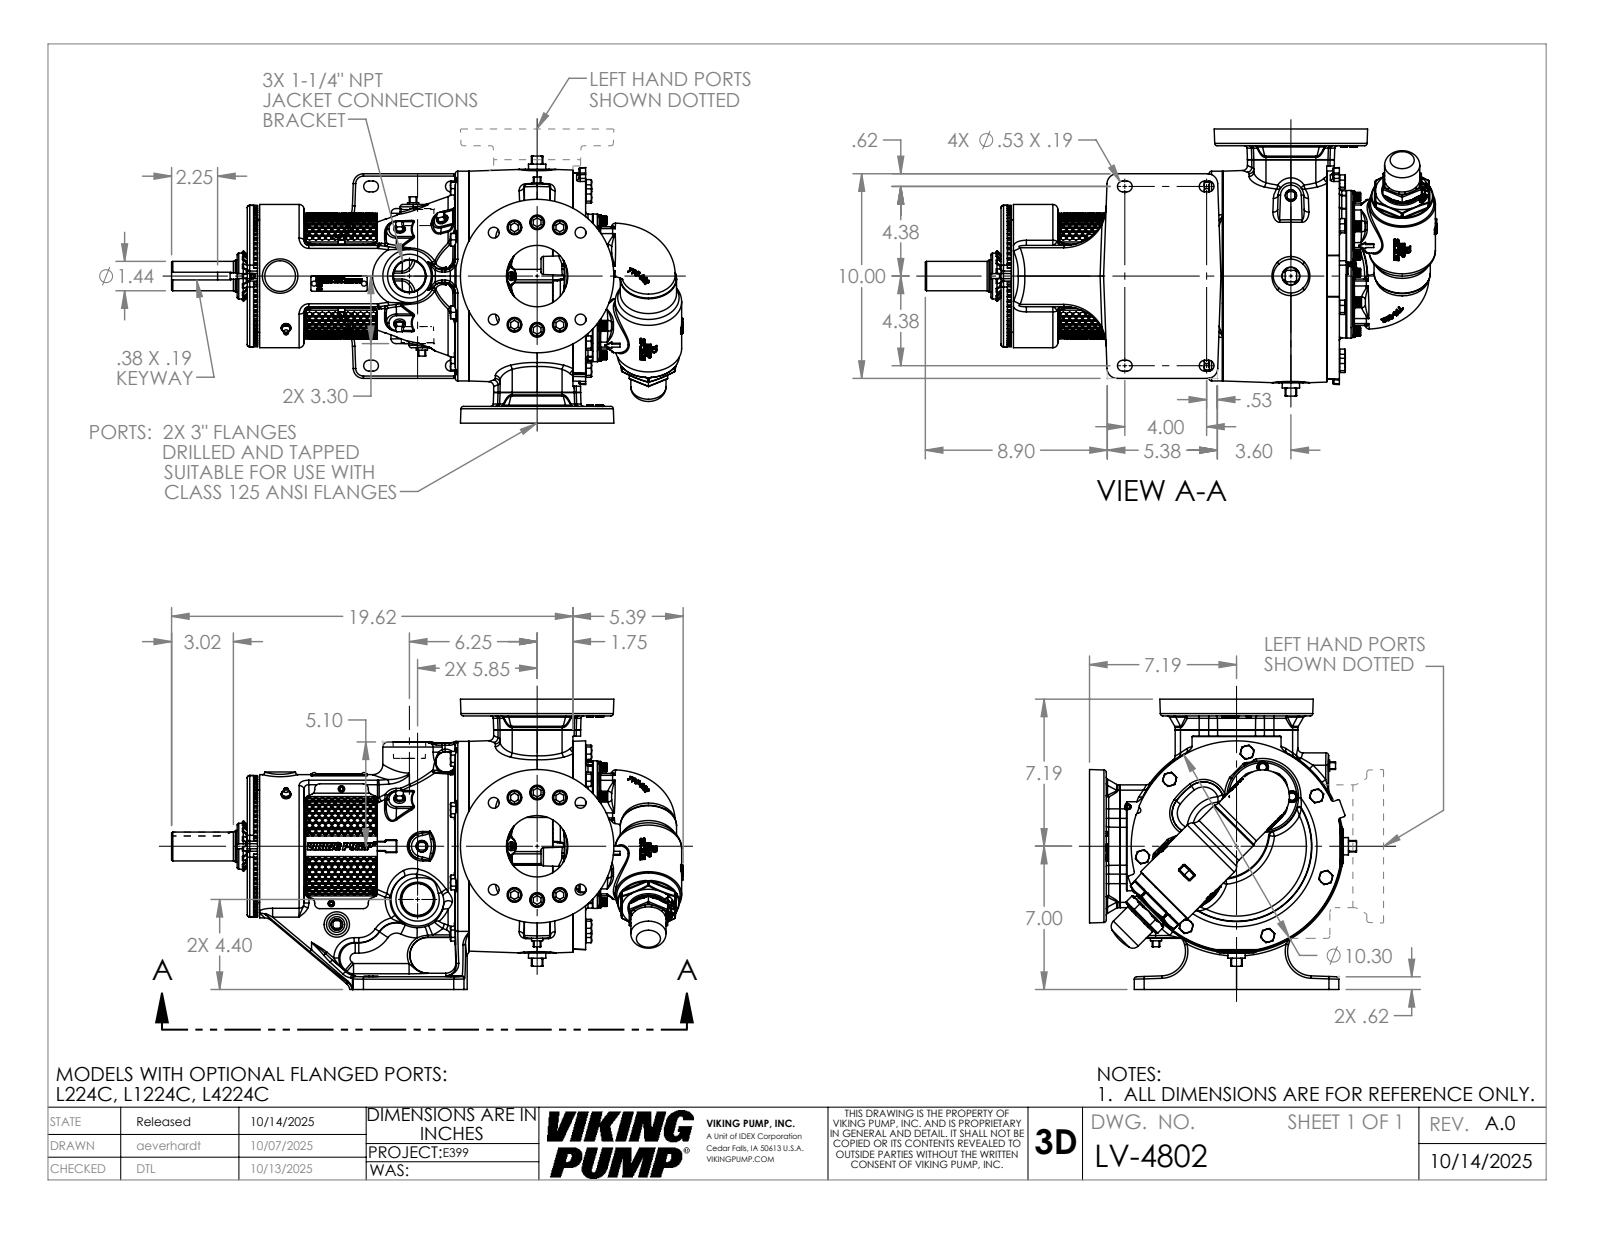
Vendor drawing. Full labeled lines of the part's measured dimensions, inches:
Part name (STEP PRODUCT): LV-4802
STEP written by: SolidWorks 2024 (AUTOMOTIVE_DESIGN)
Units: inches
Bodies: 1 solid, 6047 faces (1894 planar, 1147 cylindrical, 3006 other)
Overall size (bounding box): 25.01 × 14.188 × 13.053
Volume: 1 077 in³ · Surface area: 1 482 in²
Round holes (diameter × count): ⌀0.719 ×12, ⌀0.531 ×8, ⌀1.094 ×8, ⌀0.199 ×6, ⌀0.25 ×6, ⌀0.159 ×3, ⌀0.266 ×2, ⌀0.313 ×2, ⌀3 ×2, ⌀0.453 ×1, ⌀1.552 ×1, ⌀1.577 ×1
Round bosses / shafts (diameter × count): ⌀0.66 ×12, ⌀0.625 ×9, ⌀0.563 ×8, ⌀0.625 ×6, ⌀3.5 ×3, ⌀0.437 ×3, ⌀0.312 ×3, ⌀10.25 ×1
Partial cylindrical surfaces — rounded edges, fillets, slot ends (radius × count): R0.063 ×109, R0.069 ×74, R0.12 ×64, R0.03 ×36, R0.01 ×30, R0.009 ×26, R0.5 ×26, R0.24 ×16
Main face-to-face distances: 14.187, 0.82, 13.792, 2.25, 3.537, 10.255, 2.75, 0.5, 2.143, 5.68
Hole centre spacings: 3, 4.243, 2.625, 1.375, 1.044, 1.136, 2.18, 2.18
